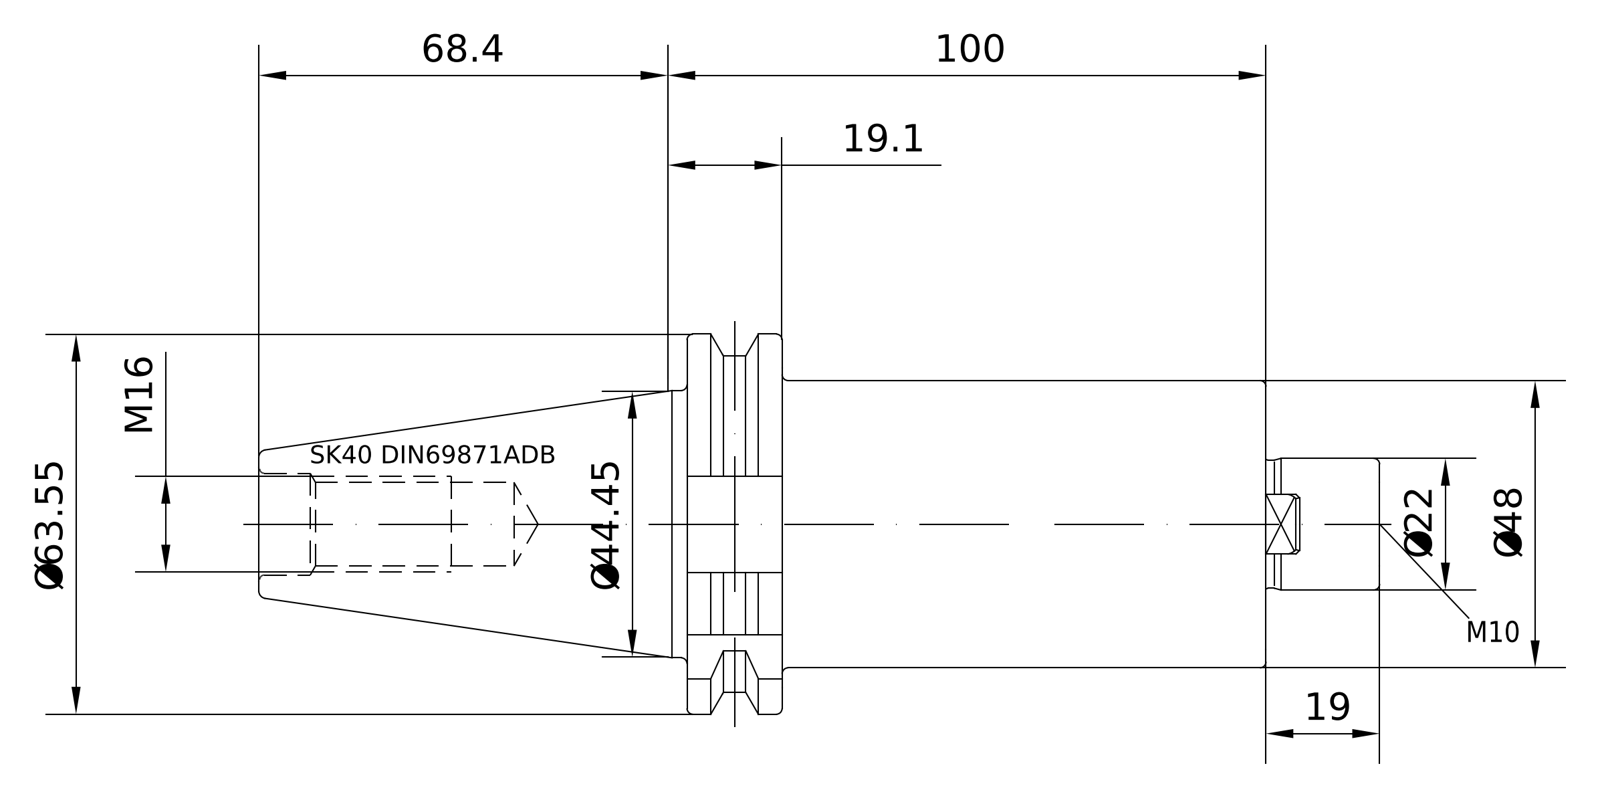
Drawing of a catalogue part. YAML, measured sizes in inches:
part_name: "40-351-22"
step_written_by: "PRO/ENGINEER BY PARAMETRIC TECHNOLOGY CORPORATION, 2010430 (CONFIG_CONTROL_DESIGN)"
units: inches
bodies: {solids: 1, faces: 115, planar: 34, cylindrical: 32, other: 49}
overall_size: [7.372, 2.501, 2.418]
volume: 15.79
surface_area: 54.72
round_holes:
  - {diameter: 0.335, count: 1}
  - {diameter: 0.394, count: 1}
  - {diameter: 0.545, count: 1}
  - {diameter: 0.67, count: 1}
  - {diameter: 0.689, count: 1}
round_bosses_or_shafts:
  - {diameter: 1.89, count: 1}
  - {diameter: 1.722, count: 1}
  - {diameter: 0.866, count: 1}
  - {diameter: 0.63, count: 1}
partial_cylinders:
  - {radius: 0.053, count: 5}
  - {radius: 1.102, count: 1}
  - {radius: 1.25, count: 1}
face_to_face_distances: [3.811, 0.624, 3.187, 4.559, 3.935, 0.748, 0.394, 0.122, 0.516, 1.866]
